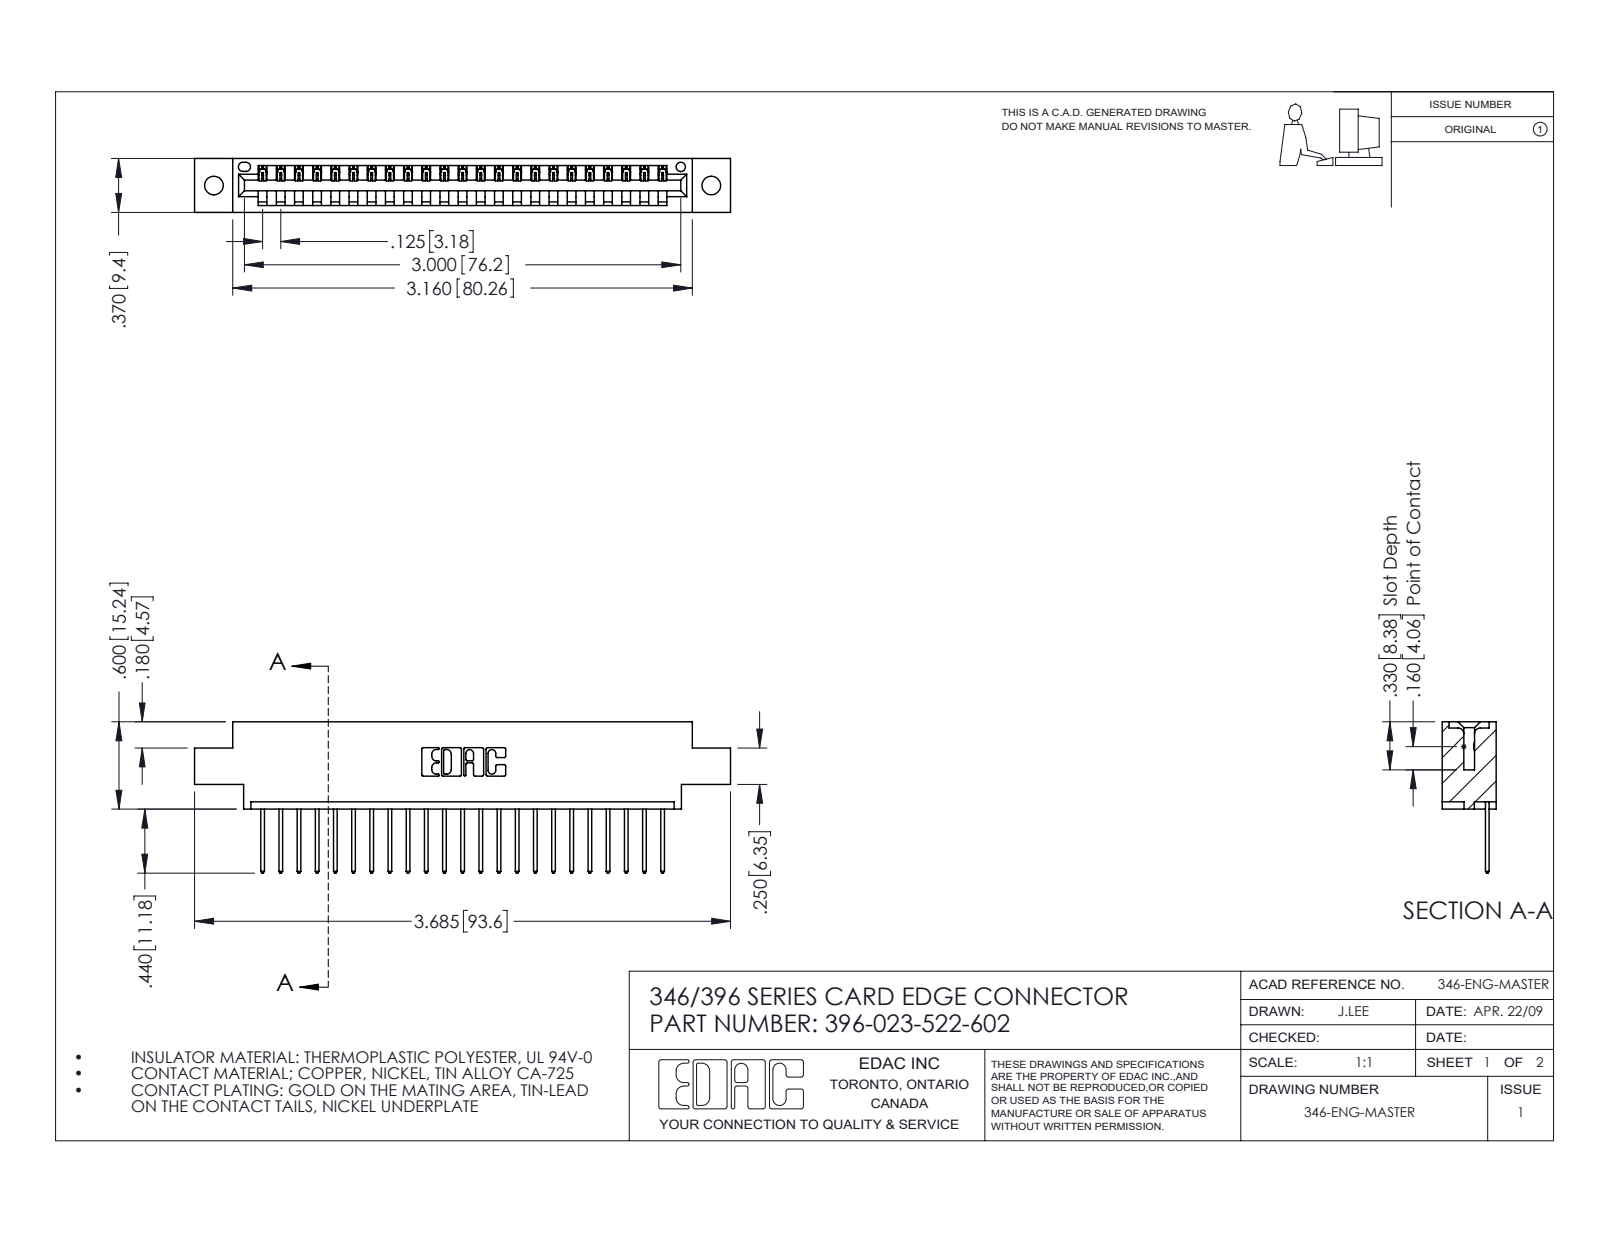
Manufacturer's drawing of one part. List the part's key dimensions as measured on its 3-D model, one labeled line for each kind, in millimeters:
Part name (STEP PRODUCT): 345-292-001_345-293-122; 396-023-522-602; 346 Part_0.170 Offset - 0.128 Dia
STEP written by: SolidWorks 2016 (CONFIG_CONTROL_DESIGN)
Units: millimetres
Bodies: 24 solids, 1460 faces (1000 planar, 460 cylindrical, 0 other)
Overall size (bounding box): 93.6 × 26.4 × 9.4
Volume: 8 640 mm³ · Surface area: 10 570 mm²
Round holes (diameter × count): ⌀3.3 ×2, ⌀1.6 ×1
Partial cylindrical surfaces — rounded edges, fillets, slot ends (radius × count): R0.2 ×46, R0.3 ×46, R0.3 ×22, R0.2 ×6, R0.8 ×6, R0.7 ×3, R0.8 ×2, R1 ×2
Main face-to-face distances: 1.2, 8.2, 9.4, 6.4, 1.8, 7.6, 0.6, 3.8, 5.6, 2.5
Hole centre spacings: 6.2, 81.6, 86.9
